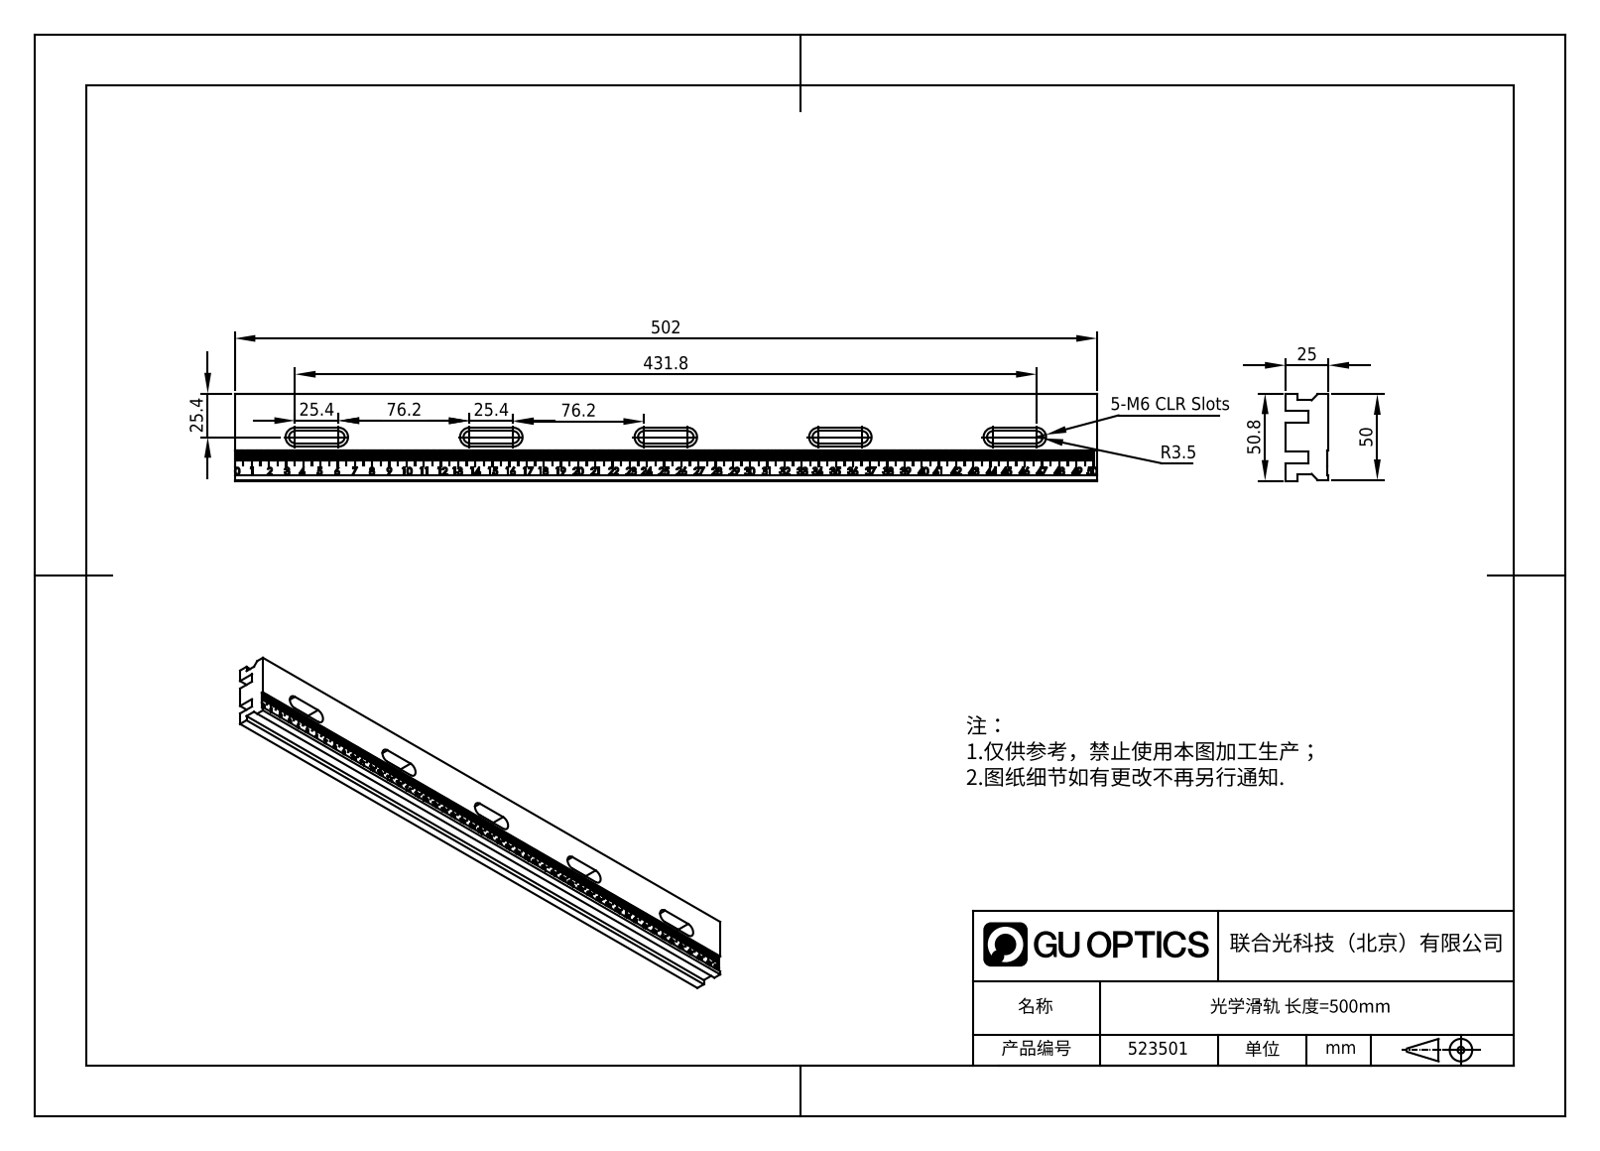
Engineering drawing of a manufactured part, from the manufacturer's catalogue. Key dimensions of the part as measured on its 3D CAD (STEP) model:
Part name (STEP PRODUCT): ORL-50
STEP written by: SolidWorks 2012 (CONFIG_CONTROL_DESIGN)
Units: millimetres
Bodies: 1 solid, 3300 faces (2703 planar, 20 cylindrical, 577 other)
Overall size (bounding box): 502 × 50.8 × 25
Volume: 458 816 mm³ · Surface area: 117 959 mm²
Partial cylindrical surfaces — rounded edges, fillets, slot ends (radius × count): R3.5 ×10, R5.5 ×10
Main face-to-face distances: 25, 7.1, 23.7, 6, 11, 13.1, 29.7, 36.8, 1, 10
